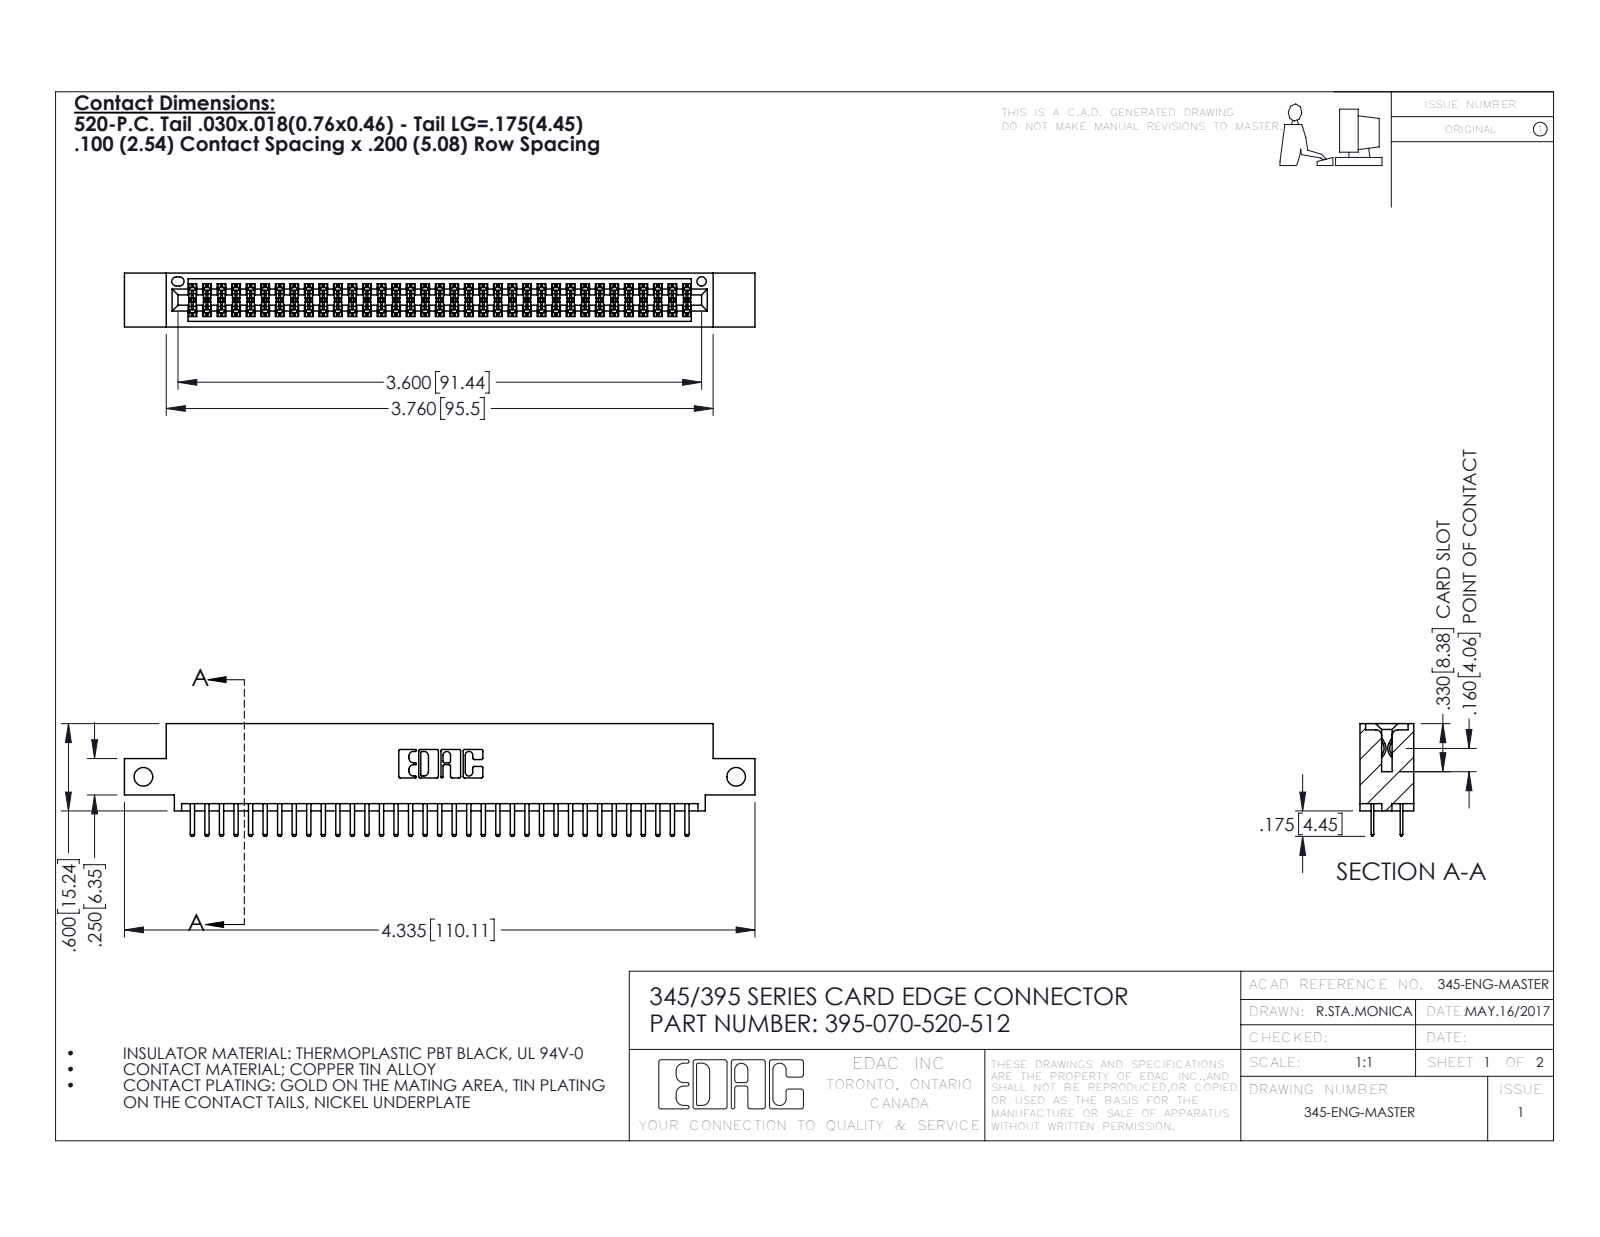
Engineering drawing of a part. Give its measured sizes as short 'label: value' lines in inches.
name: 345 Part_0.110 Offset - Side Mount; 395-070-520-512; 345-292-001_345-293-120
written by: SolidWorks 2016 (CONFIG_CONTROL_DESIGN)
unit: in
bodies: 71 solids, 3910 faces (2534 planar, 1376 cylindrical, 0 other)
size: 4.335 × 0.775 × 0.37
volume: 0.637 in³; area: 23.54 in²
holes: 2× ⌀0.128, 1× ⌀0.064
rounds: 105× R0.006, 74× R0.01, 22× R0.01, 6× R0.007, 6× R0.031, 3× R0.026, 2× R0.014, 2× R0.019
face distances: 0.298, 0.072, 0.2, 0.37, 0.098, 0.272, 0.025, 0.225, 0.022, 0.072
hole spacings: 4.075
